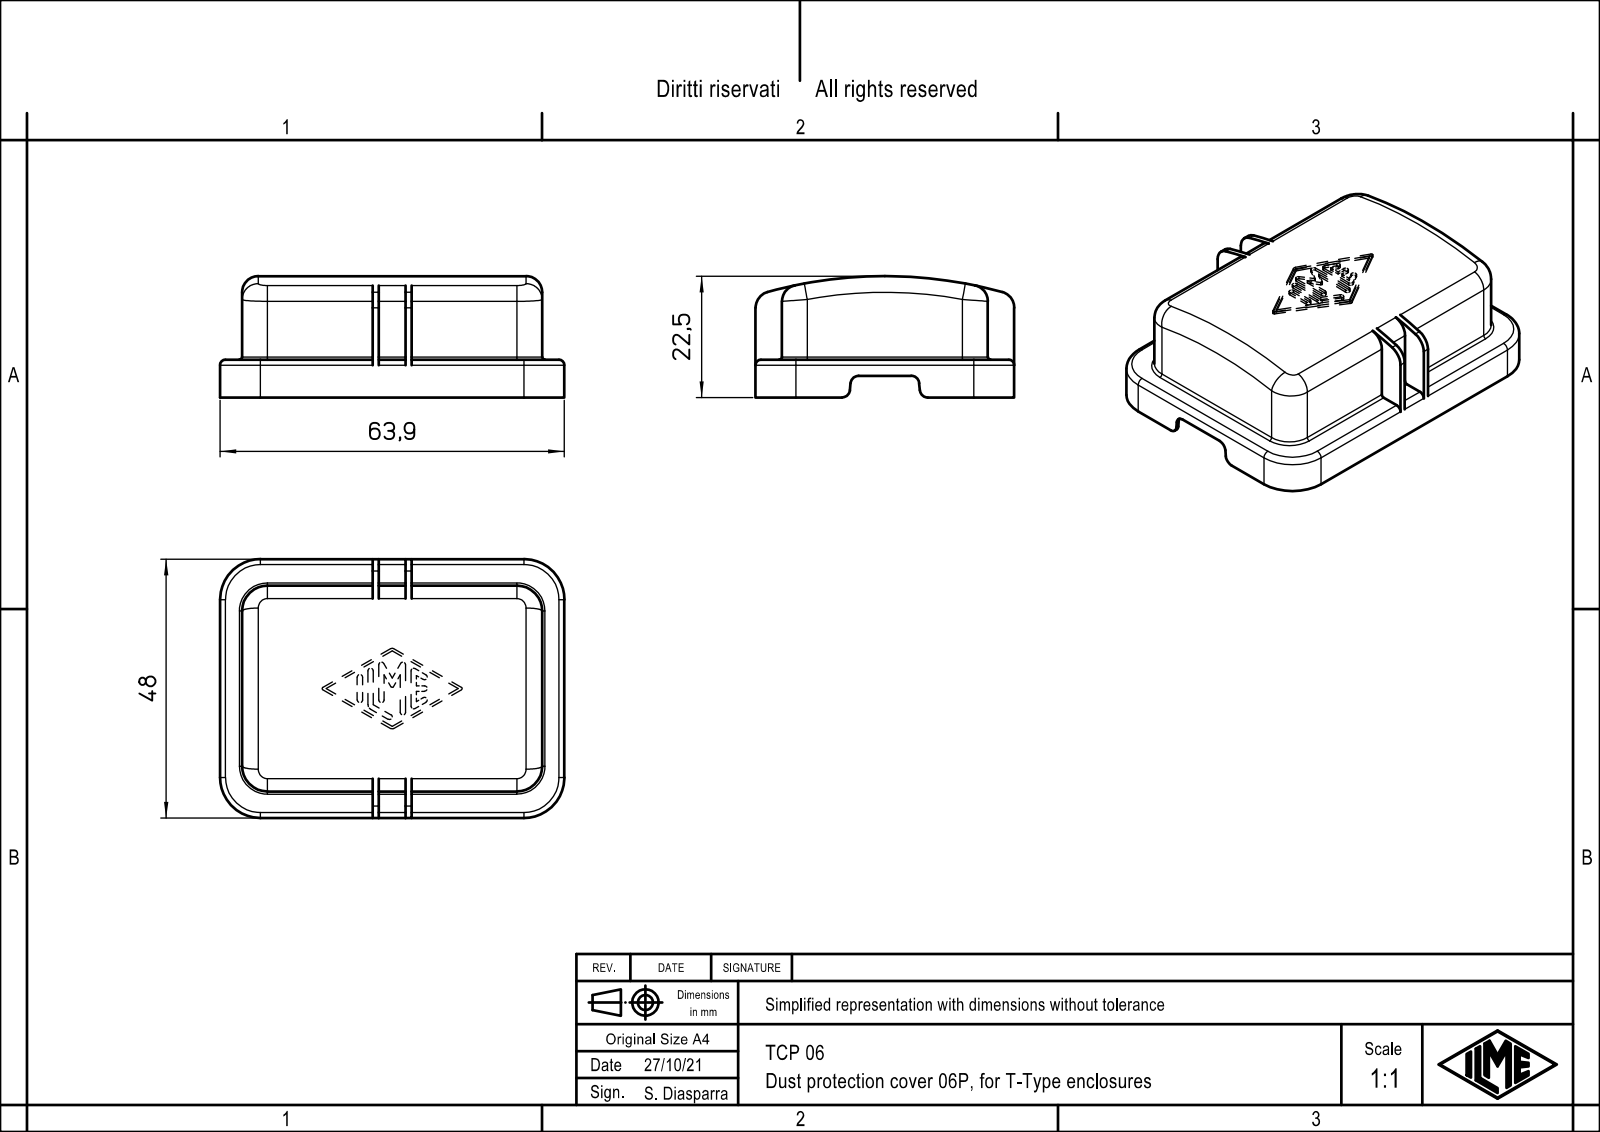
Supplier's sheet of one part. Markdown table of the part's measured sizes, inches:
| quantity | value |
| --- | --- |
| part name | TCP_06 |
| STEP written by | Creo Elements/Direct Modeling 20.1B 02-Apr-2019 (C) Parametric Technology GmbH (AUTOMOTIVE_DESIGN) |
| units | inches |
| bodies | 1 solid, 179 faces (72 planar, 83 cylindrical, 24 other) |
| overall size | 2.516 × 1.89 × 0.886 |
| volume | 0.415 in³ |
| surface area | 21.18 in² |
| partial cylindrical surfaces (radius × count) | 0.02 × 23, 0.118 × 8, 0.039 × 5, 0.059 × 4, 0.185 × 4, 0.276 × 4, 0.295 × 4, 0.01 × 3 |
| main face-to-face distances | 0.043, 0.039, 1.461, 0.236, 0.197, 2.15, 0.193, 1.654, 1.697, 1.417 |
